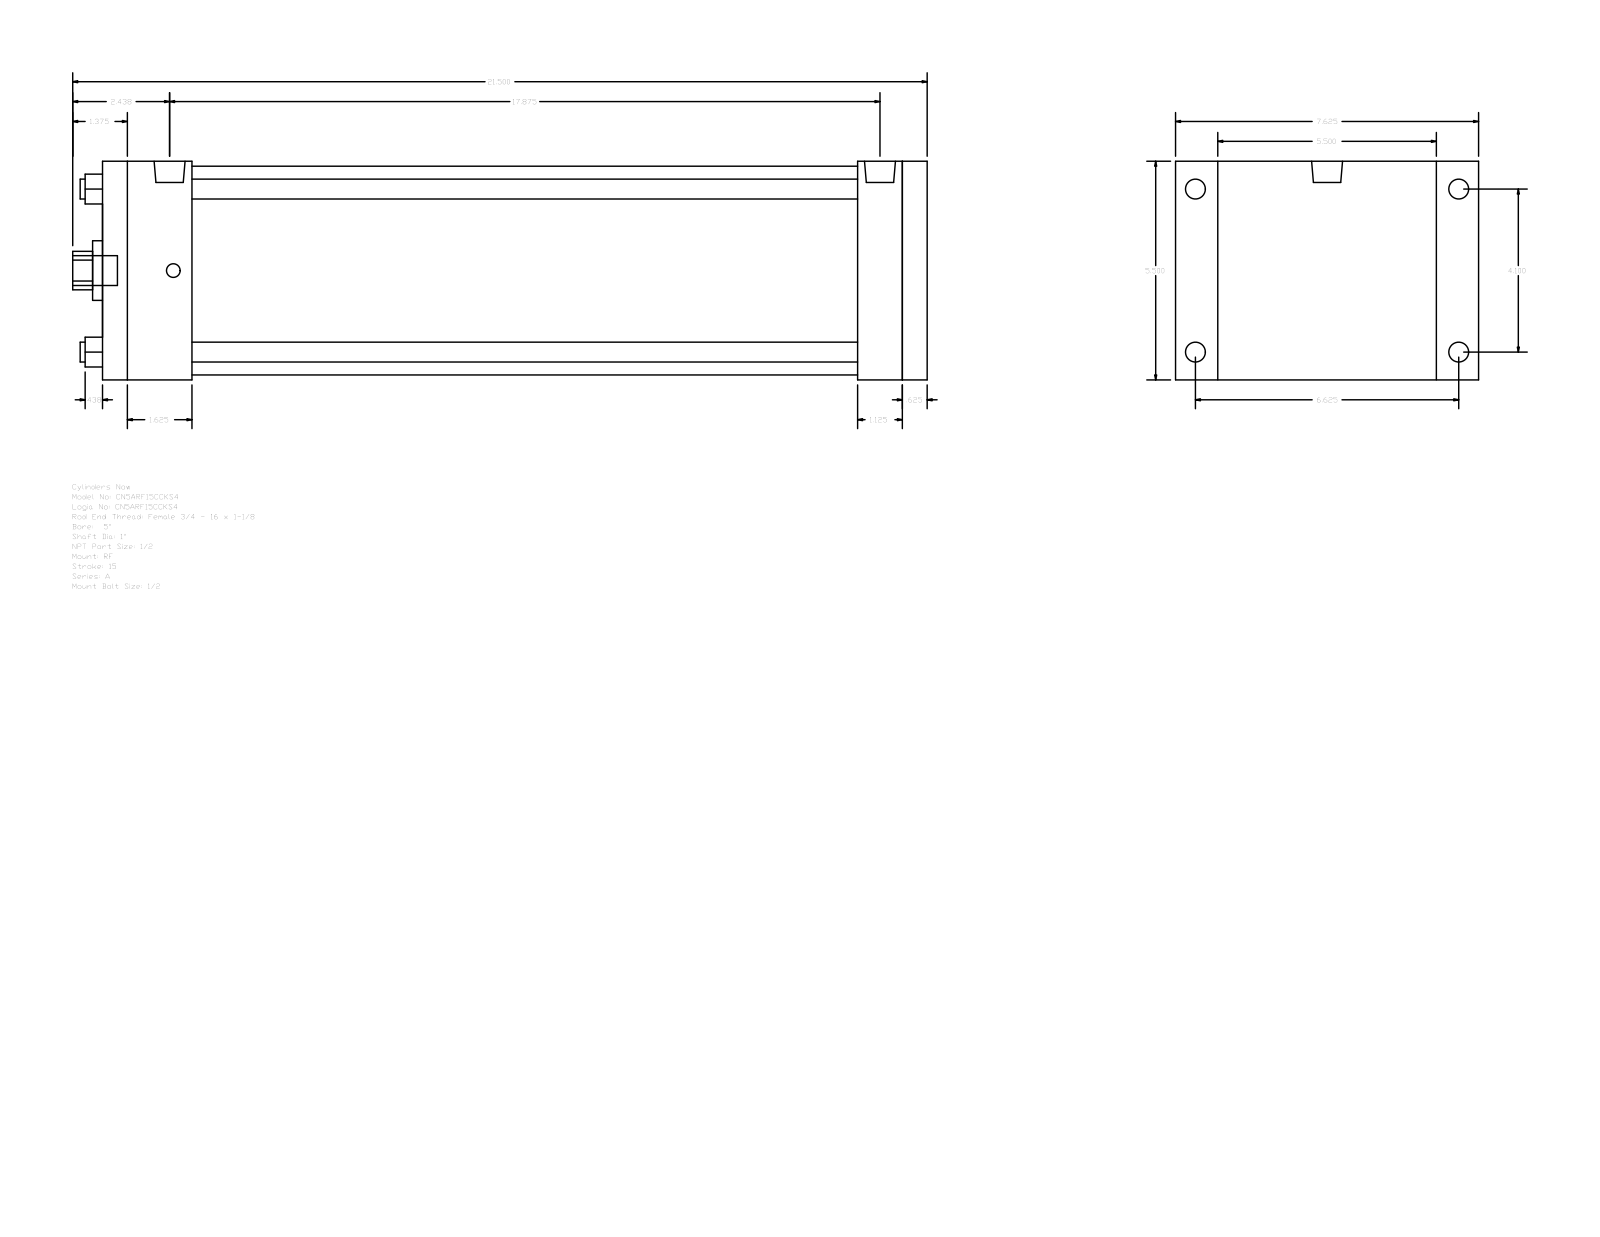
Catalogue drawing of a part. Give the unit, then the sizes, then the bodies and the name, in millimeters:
Units: millimetres
Overall size (bounding box): 546.1 × 193.68 × 139.7
Round holes (diameter × count): ⌀12.7 ×4, ⌀25.4 ×1, ⌀38.1 ×1, ⌀133.35 ×1
Round bosses / shafts (diameter × count): ⌀12.7 ×4, ⌀8.73 ×4, ⌀19.77 ×2, ⌀19.05 ×1
Partial cylindrical surfaces — rounded edges, fillets, slot ends (radius × count): R12.29 ×1
Main face-to-face distances: 139.7, 527.05, 15.87, 511.18, 57.15, 454.03, 469.9, 482.6, 425.45, 28.58
Hole centre spacings: 73.64, 104.14, 147.28
Bodies: 0 solids, 92 faces (64 planar, 28 cylindrical, 0 other)
Part name (STEP PRODUCT): A_RF__0500_1
STEP written by: GSSL Pune (CONFIG_CONTROL_DESIGN)
